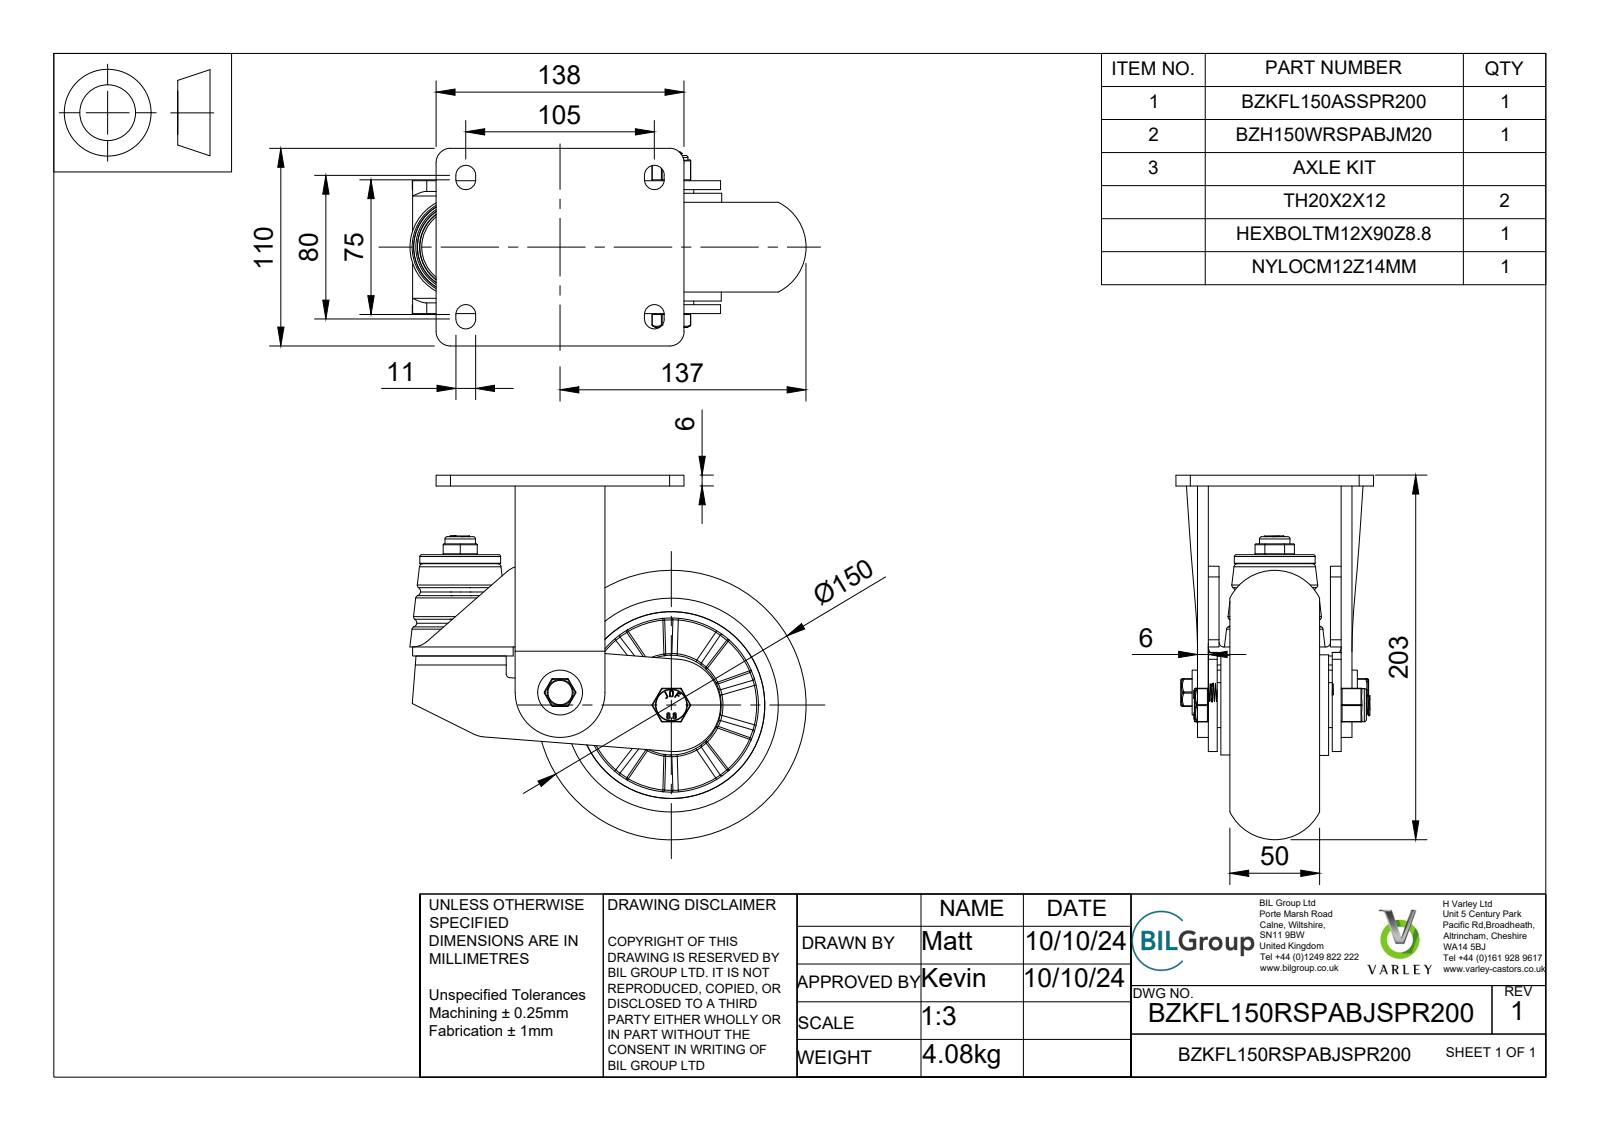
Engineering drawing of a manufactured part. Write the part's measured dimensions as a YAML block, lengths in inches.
part_name: "BZKFL150RSPABJSPR200 v3; BZKFL150ASSPR200 v1; BZKFL150ASSPR200; FABRICATED STEEL BRACKET (+8 more)"
step_written_by: "Autodesk Translation Framework v13.20.0.188 (AUTOMOTIVE_DESIGN)"
units: inches
bodies: {solids: 47, faces: 1565, planar: 505, cylindrical: 365, other: 695}
overall_size: [8.685, 7.992, 4.331]
volume: 60.29
surface_area: 502.6
round_holes:
  - {diameter: 0.472, count: 2}
  - {diameter: 0.394, count: 1}
  - {diameter: 0.48, count: 1}
  - {diameter: 0.502, count: 1}
  - {diameter: 0.551, count: 1}
  - {diameter: 0.787, count: 1}
  - {diameter: 1.122, count: 1}
  - {diameter: 1.213, count: 1}
  - {diameter: 1.575, count: 1}
  - {diameter: 1.587, count: 1}
  - {diameter: 1.594, count: 1}
  - {diameter: 1.654, count: 1}
round_bosses_or_shafts:
  - {diameter: 0.984, count: 2}
  - {diameter: 2.205, count: 1}
  - {diameter: 2.185, count: 1}
  - {diameter: 1.969, count: 1}
  - {diameter: 1.772, count: 1}
  - {diameter: 1.606, count: 1}
  - {diameter: 1.232, count: 1}
  - {diameter: 1.063, count: 1}
partial_cylinders:
  - {radius: 0.02, count: 37}
  - {radius: 0.217, count: 8}
  - {radius: 0.03, count: 6}
  - {radius: 0.039, count: 6}
  - {radius: 0.019, count: 4}
  - {radius: 0.035, count: 4}
  - {radius: 0.197, count: 4}
  - {radius: 0.315, count: 4}
face_to_face_distances: [0.236, 0.197, 2.441, 0.472, 2.717, 2.913, 0.276, 0.709, 2.677, 1.969]
hole_center_spacings: [2.456]
